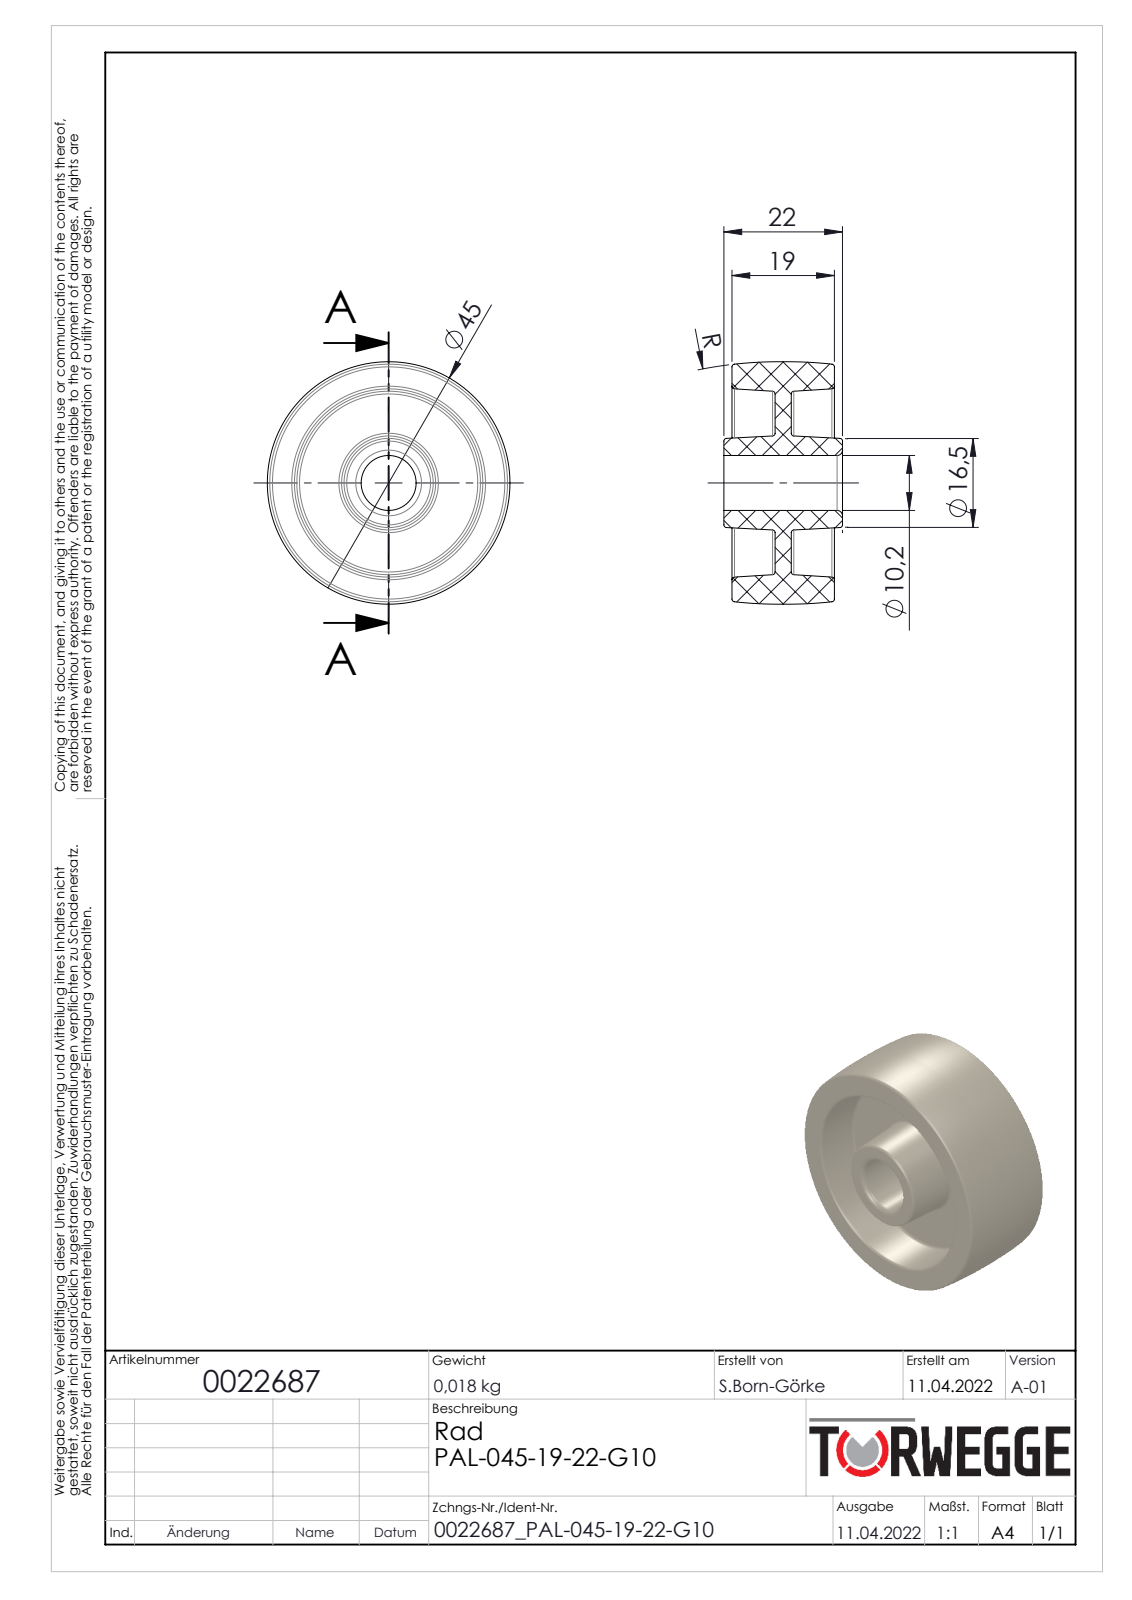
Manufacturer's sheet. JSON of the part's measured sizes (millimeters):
{"part_name": "0022687", "step_written_by": "SolidWorks 2020 (AUTOMOTIVE_DESIGN)", "units": "millimeters", "bodies": {"solids": 1, "faces": 42, "planar": 6, "cylindrical": 2, "other": 34}, "overall_size": [45.01, 45.01, 22], "volume_mm3": 17360, "surface_area_mm2": 8669, "round_holes": [[10.2, 1]], "face_to_face_distances": [8, 11, 3, 19, 1.5, 9.5, 12.5, 20.5, 22]}
